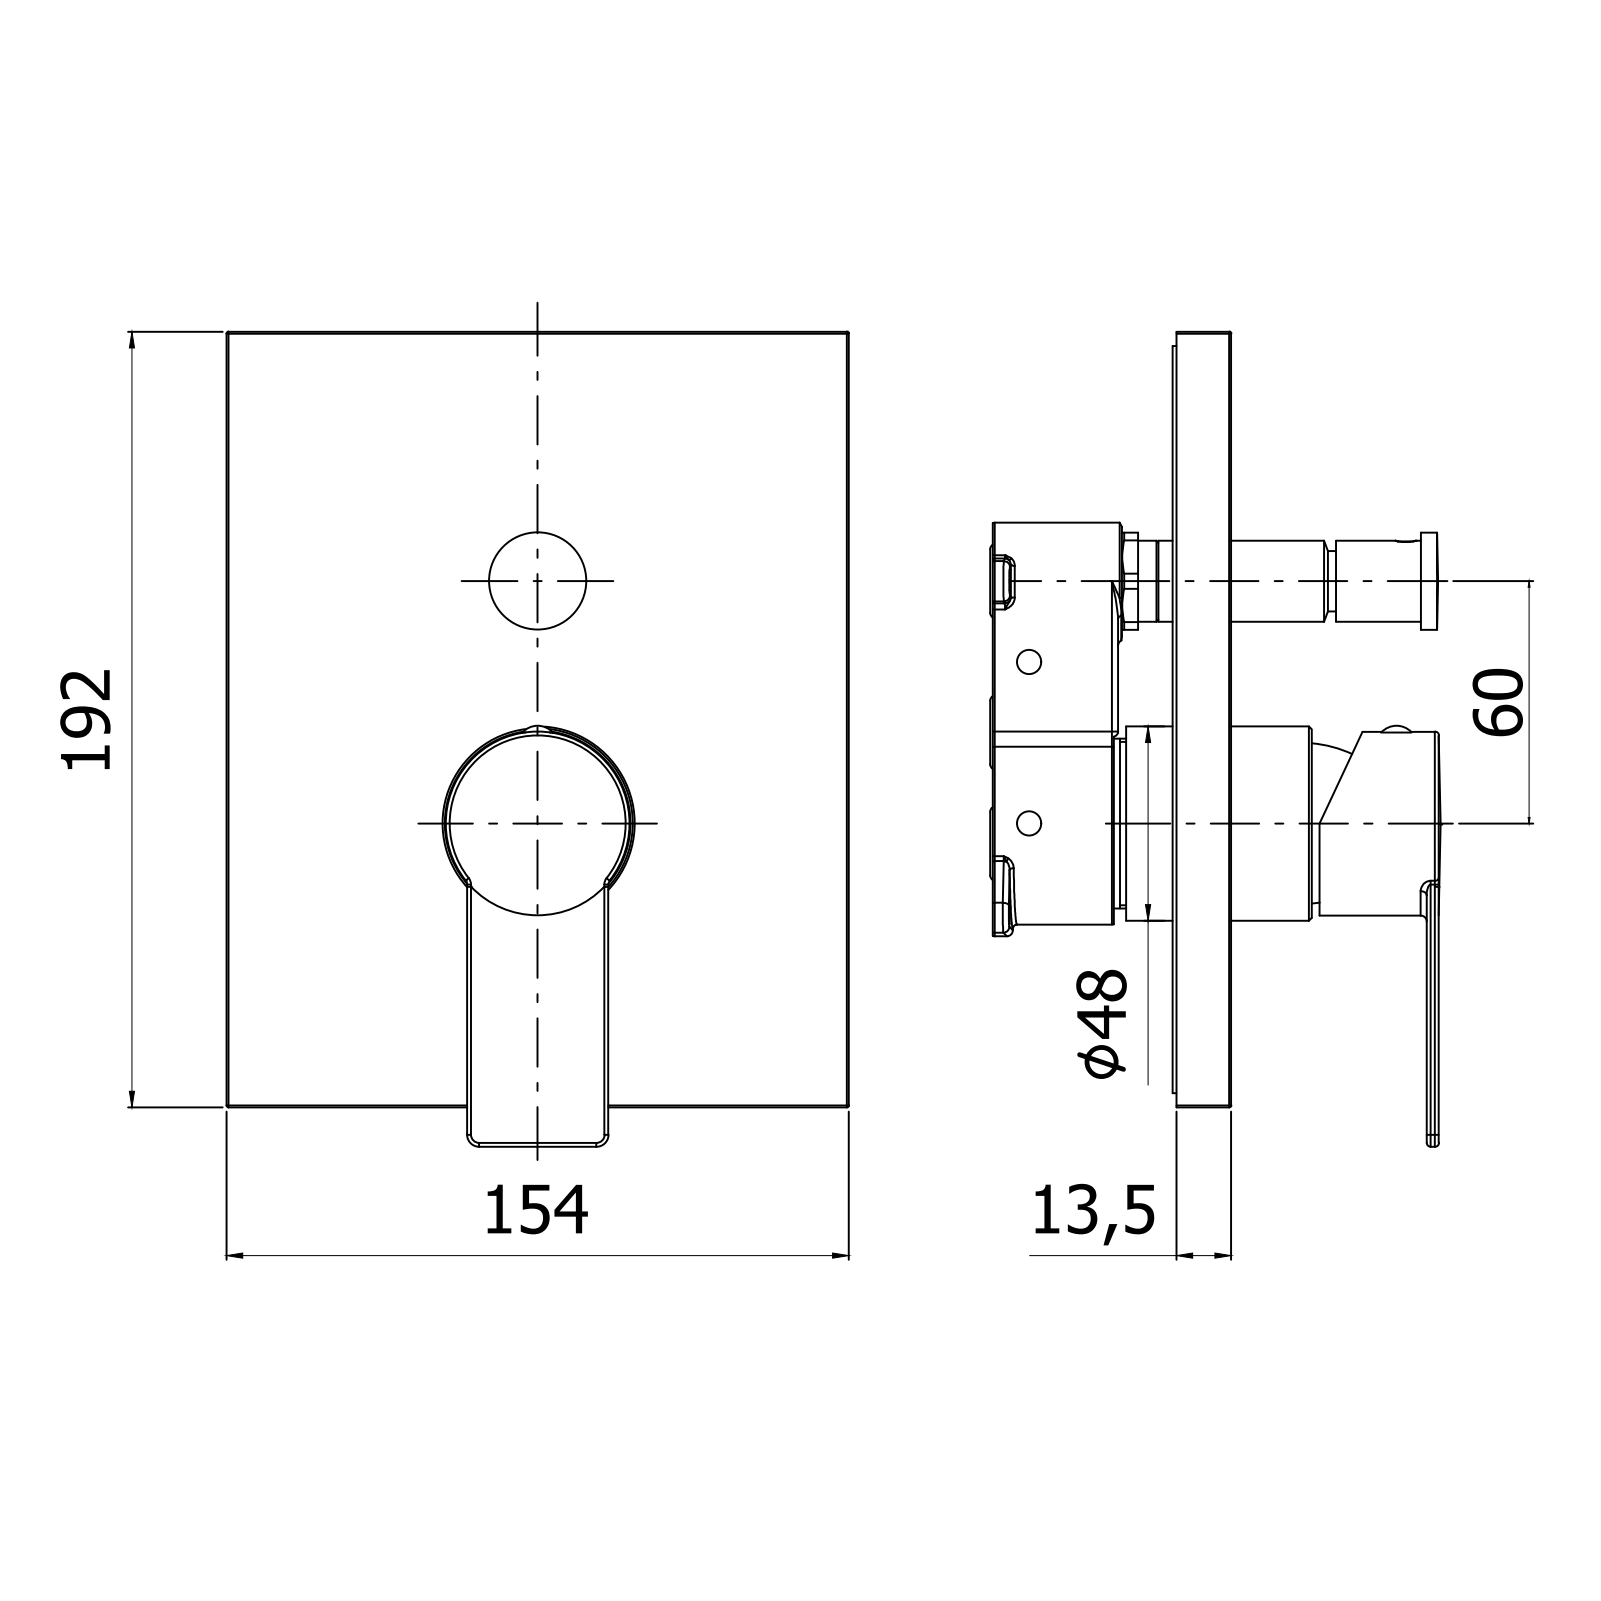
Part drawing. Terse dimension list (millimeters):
name: TABOX015CR
written by: CREO PARAMETRIC BY PTC INC, 2020044 (CONFIG_CONTROL_DESIGN)
unit: mm
bodies: 2 solids, 178 faces (52 planar, 63 cylindrical, 63 other)
size: 201.75 × 154 × 65.6
volume: 451 889 mm³; area: 95 984 mm²
holes: 1× ⌀3, 1× ⌀4.2, 1× ⌀30.6, 1× ⌀36, 1× ⌀37.5
bosses: 1× ⌀48.1, 1× ⌀45.5, 1× ⌀24, 1× ⌀20, 1× ⌀15, 1× ⌀7.6, 1× ⌀5.5
rounds: 10× R0.5, 6× R1, 4× R1.5, 2× R3, 1× R3.5
face distances: 13.5, 154, 192, 65.1, 51.6, 3, 62.1, 48.6, 3.5, 0.5
